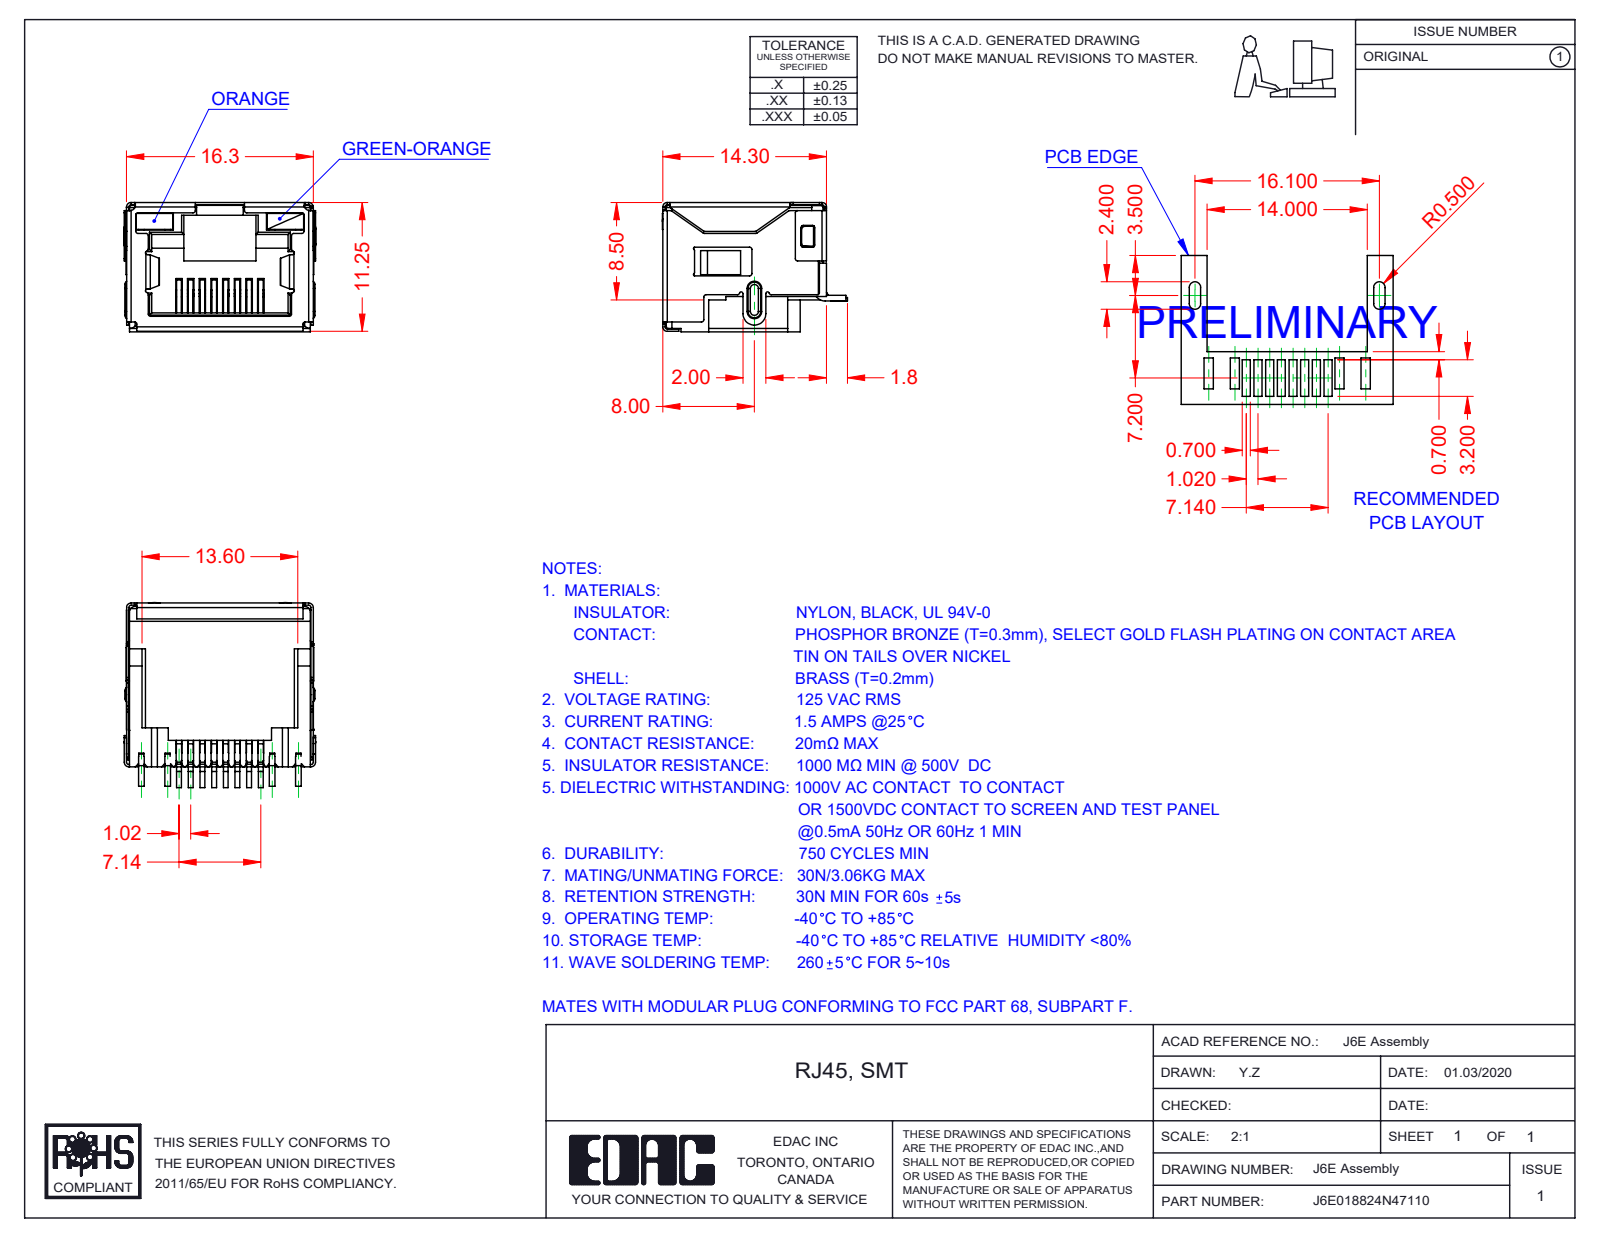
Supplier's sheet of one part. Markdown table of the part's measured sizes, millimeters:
| quantity | value |
| --- | --- |
| part name | J6E018824N47110; 6E Contacts; 6E Shield_LED; 6E LED RH_7-Green-Orange (+2 more) |
| STEP written by | SolidWorks 2016 (CONFIG_CONTROL_DESIGN) |
| units | millimeters |
| bodies | 12 solids, 1498 faces (1099 planar, 349 cylindrical, 50 other) |
| overall size | 16.75 × 16.15 × 11.3 |
| volume | 1 109 mm³ |
| surface area | 4 045 mm² |
| partial cylindrical surfaces (radius × count) | 0.2 × 82, 0.25 × 17, 0.4 × 13, 0.5 × 13, 0.1 × 10, 0.15 × 7, 0.3 × 4, 1 × 3 |
| main face-to-face distances | 11.05, 16.05, 16.1, 15.85, 11.1, 11.3, 2.4, 0.7, 9.85, 0.49 |
